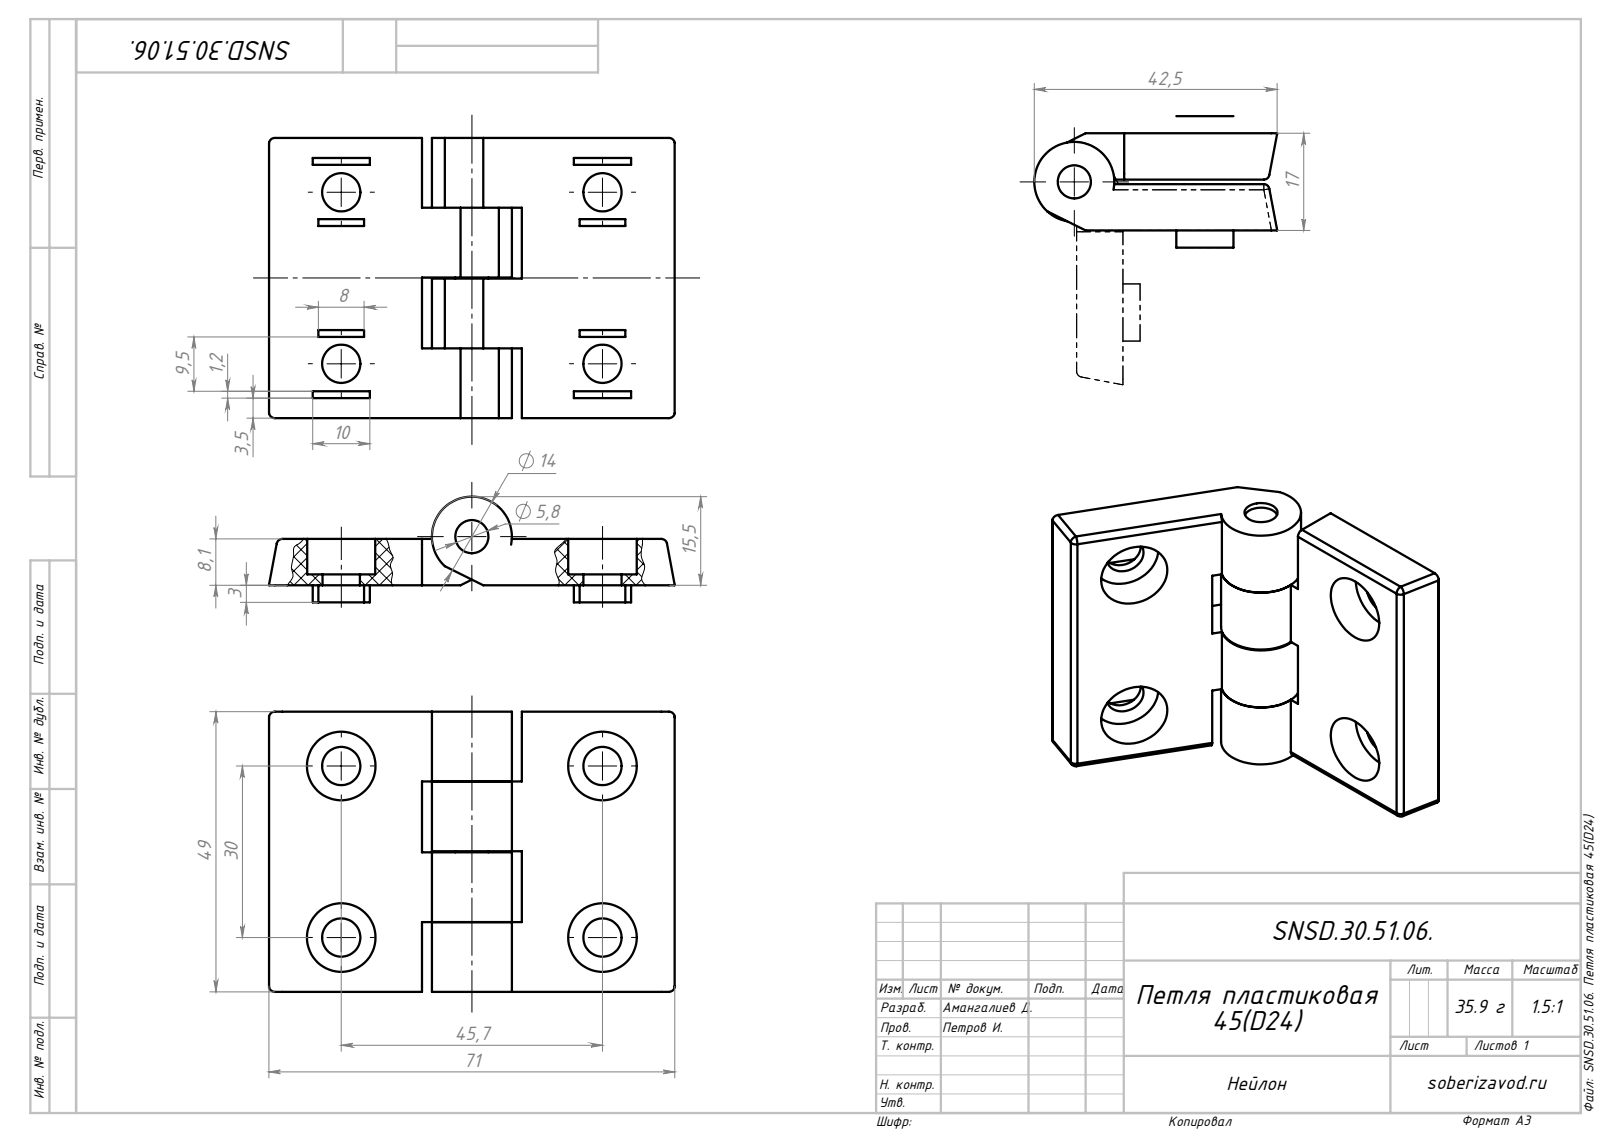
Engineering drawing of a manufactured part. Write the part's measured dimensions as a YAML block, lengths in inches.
part_name: "SNSD.30.51.00. Петля пластиковая малая часть(B18)E20E21D24_00; SNSD.30.51.06. Петля пластиковая 45(D24); SNSD.30.51.00. Палец (B18)E20E21D24_00"
step_written_by: "SolidWorks 2024 (AUTOMOTIVE_DESIGN)"
units: inches
bodies: {solids: 3, faces: 124, planar: 72, cylindrical: 48, other: 4}
overall_size: [2.794, 1.929, 0.728]
volume: 1.642
surface_area: 21.09
round_holes:
  - {diameter: 0.264, count: 4}
  - {diameter: 0.472, count: 4}
  - {diameter: 0.228, count: 1}
partial_cylinders:
  - {radius: 0.039, count: 8}
  - {radius: 0.276, count: 1}
face_to_face_distances: [0.319, 0.48, 0.969, 1.449, 1.929, 0.961, 0.488, 0.075, 0.244, 0.047]
hole_center_spacings: [1.181, 1.8, 2.153]
